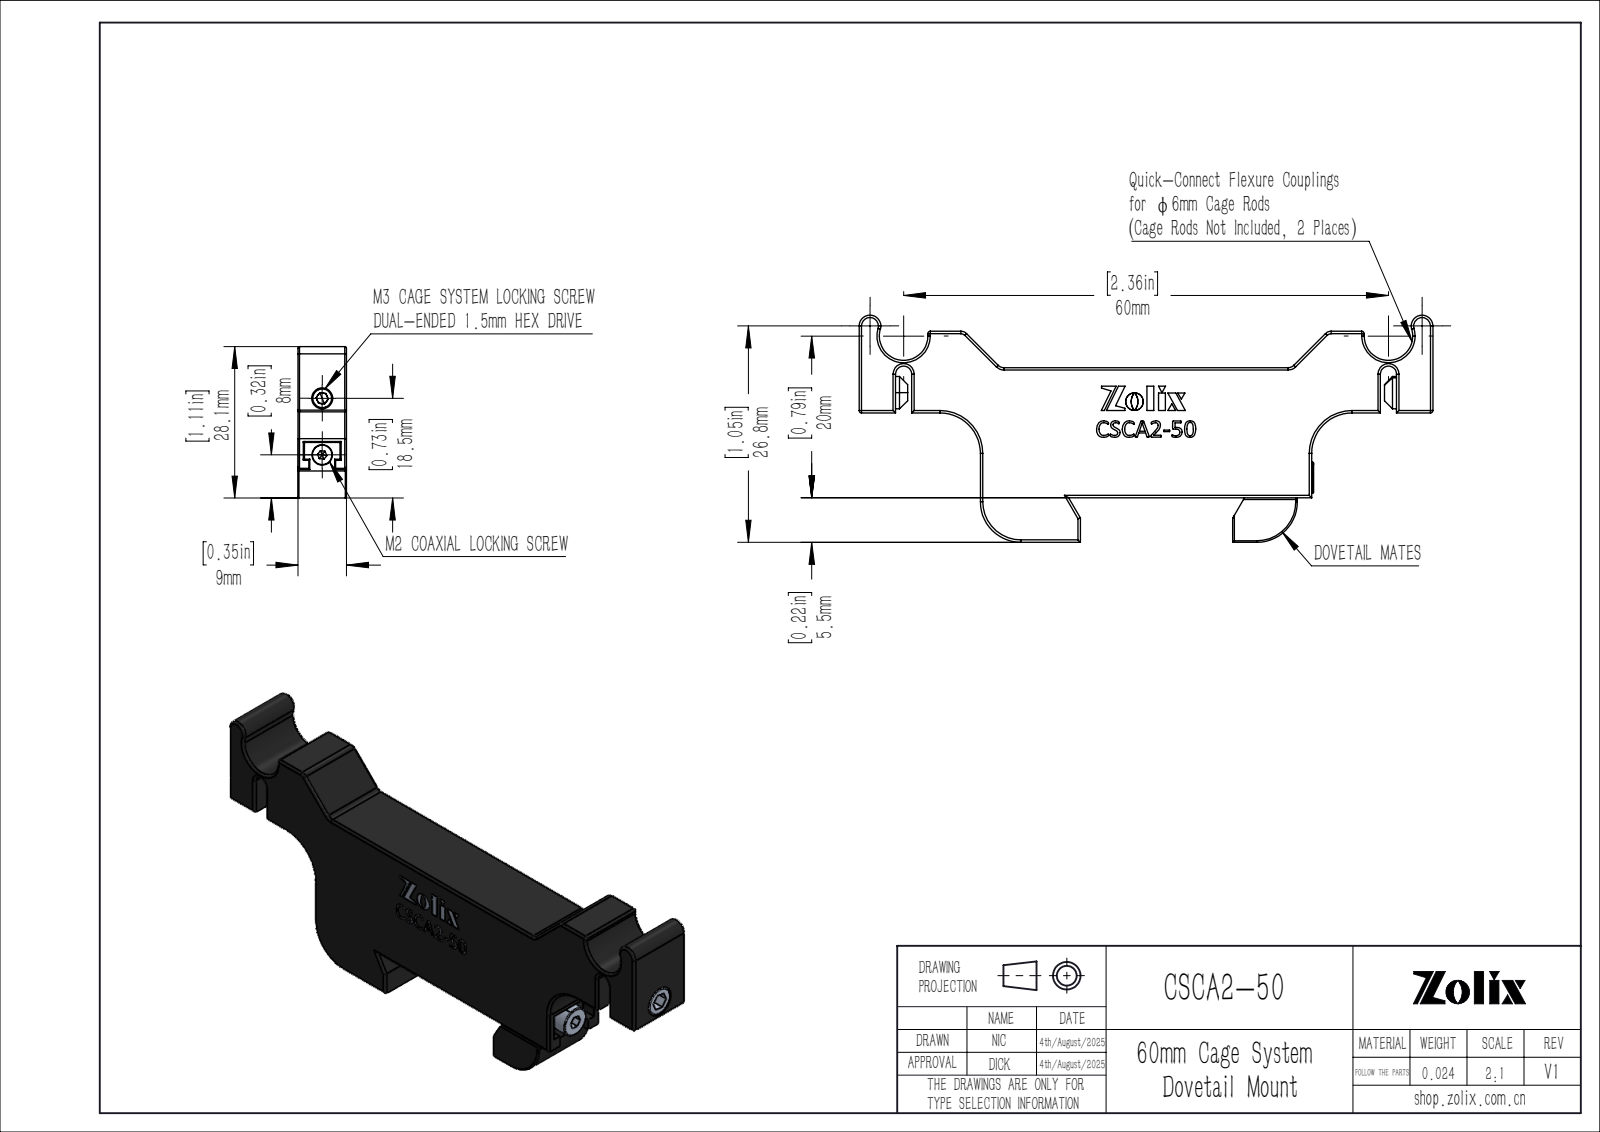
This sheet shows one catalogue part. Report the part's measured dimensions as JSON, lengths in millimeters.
{"part_name": "CSCA2-50", "step_written_by": "SolidWorks 2020 (CONFIG_CONTROL_DESIGN)", "units": "millimeters", "bodies": {"solids": 5, "faces": 562, "planar": 292, "cylindrical": 114, "other": 156}, "overall_size": [71, 28.1, 9], "volume_mm3": 9056, "surface_area_mm2": 5036, "round_holes": [[1.6, 1], [2.5, 1], [3.3, 1]], "round_bosses_or_shafts": [[4, 1], [3.8, 1], [2, 1]], "partial_cylinders_radius": [[0.3, 42], [0.2, 26], [1, 6], [5, 3], [1.34, 2], [2, 2], [3, 2], [5, 1]], "face_to_face_distances": [9, 10.5, 5.5, 16.1, 5, 1, 11.1, 8, 5.6, 7], "hole_center_spacings": [10.5]}
